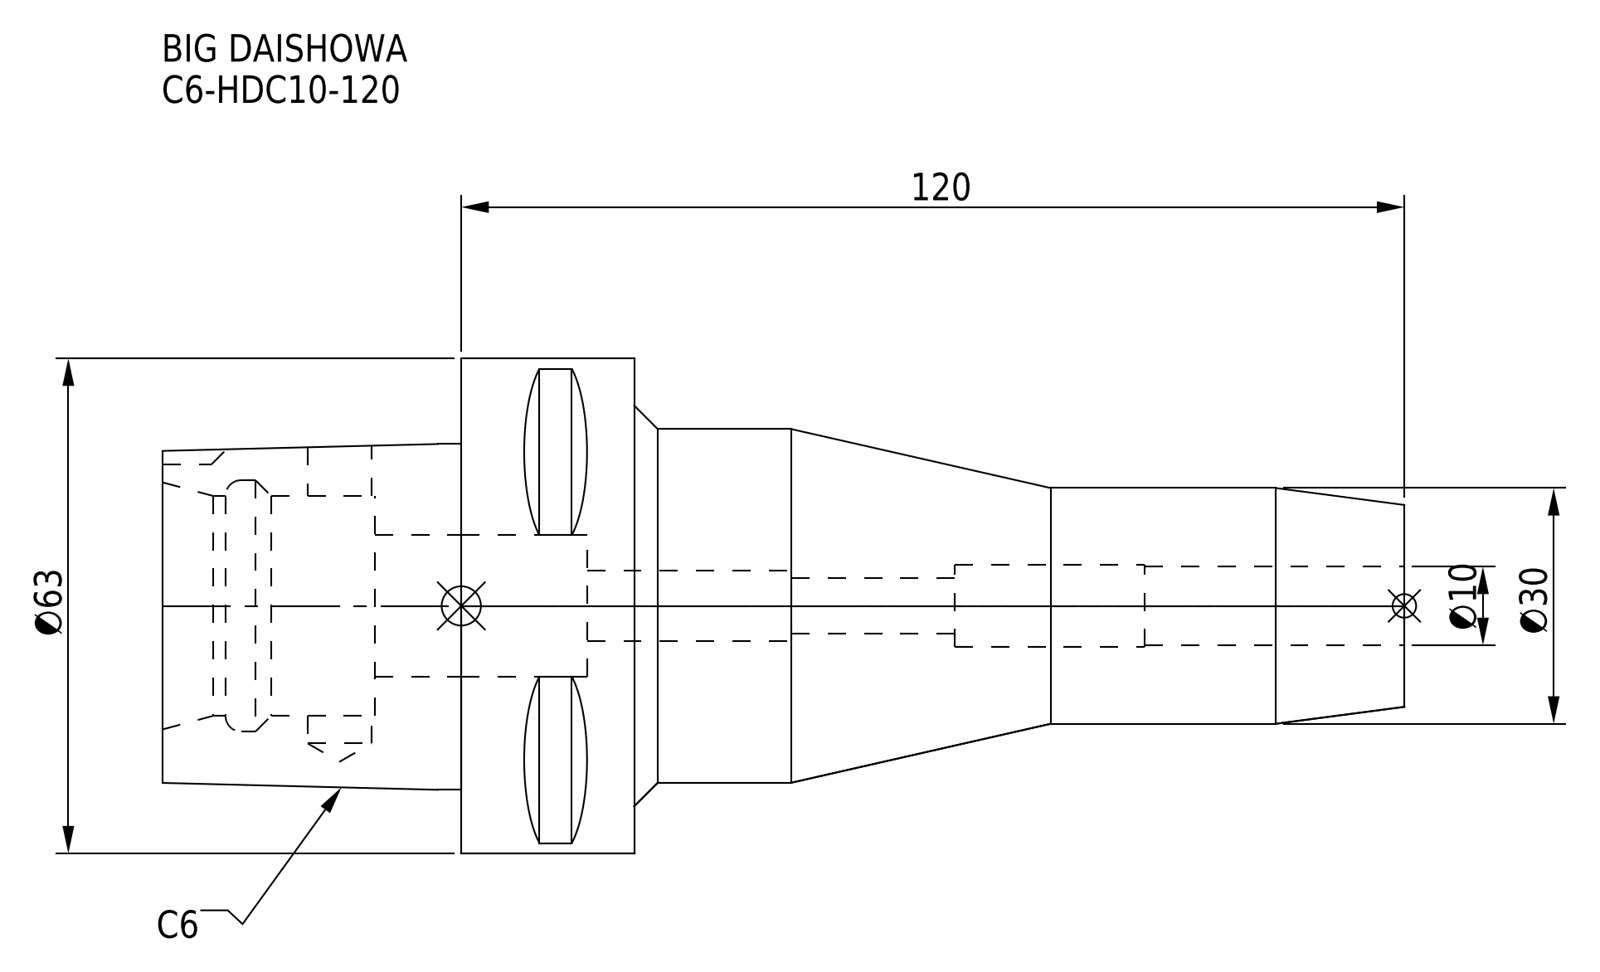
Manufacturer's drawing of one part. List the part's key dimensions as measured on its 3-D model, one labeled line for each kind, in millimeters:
Part name (STEP PRODUCT): C6-HDC10-120
STEP written by: CREO PARAMETRIC BY PTC INC, 2016380 (AUTOMOTIVE_DESIGN)
Units: millimetres
Bodies: 1 solid, 74 faces (31 planar, 27 cylindrical, 16 other)
Overall size (bounding box): 158 × 63 × 63
Volume: 189 075 mm³ · Surface area: 32 764 mm²
Round holes (diameter × count): ⌀7 ×1, ⌀8.1 ×1, ⌀9 ×1, ⌀10 ×1, ⌀10.5 ×1, ⌀18 ×1, ⌀28 ×1, ⌀32 ×1
Round bosses / shafts (diameter × count): ⌀63 ×1, ⌀45 ×1, ⌀30 ×1
Partial cylindrical surfaces — rounded edges, fillets, slot ends (radius × count): R5 ×1
Main face-to-face distances: 22, 27, 60, 38, 98, 120, 158, 33, 131, 11
